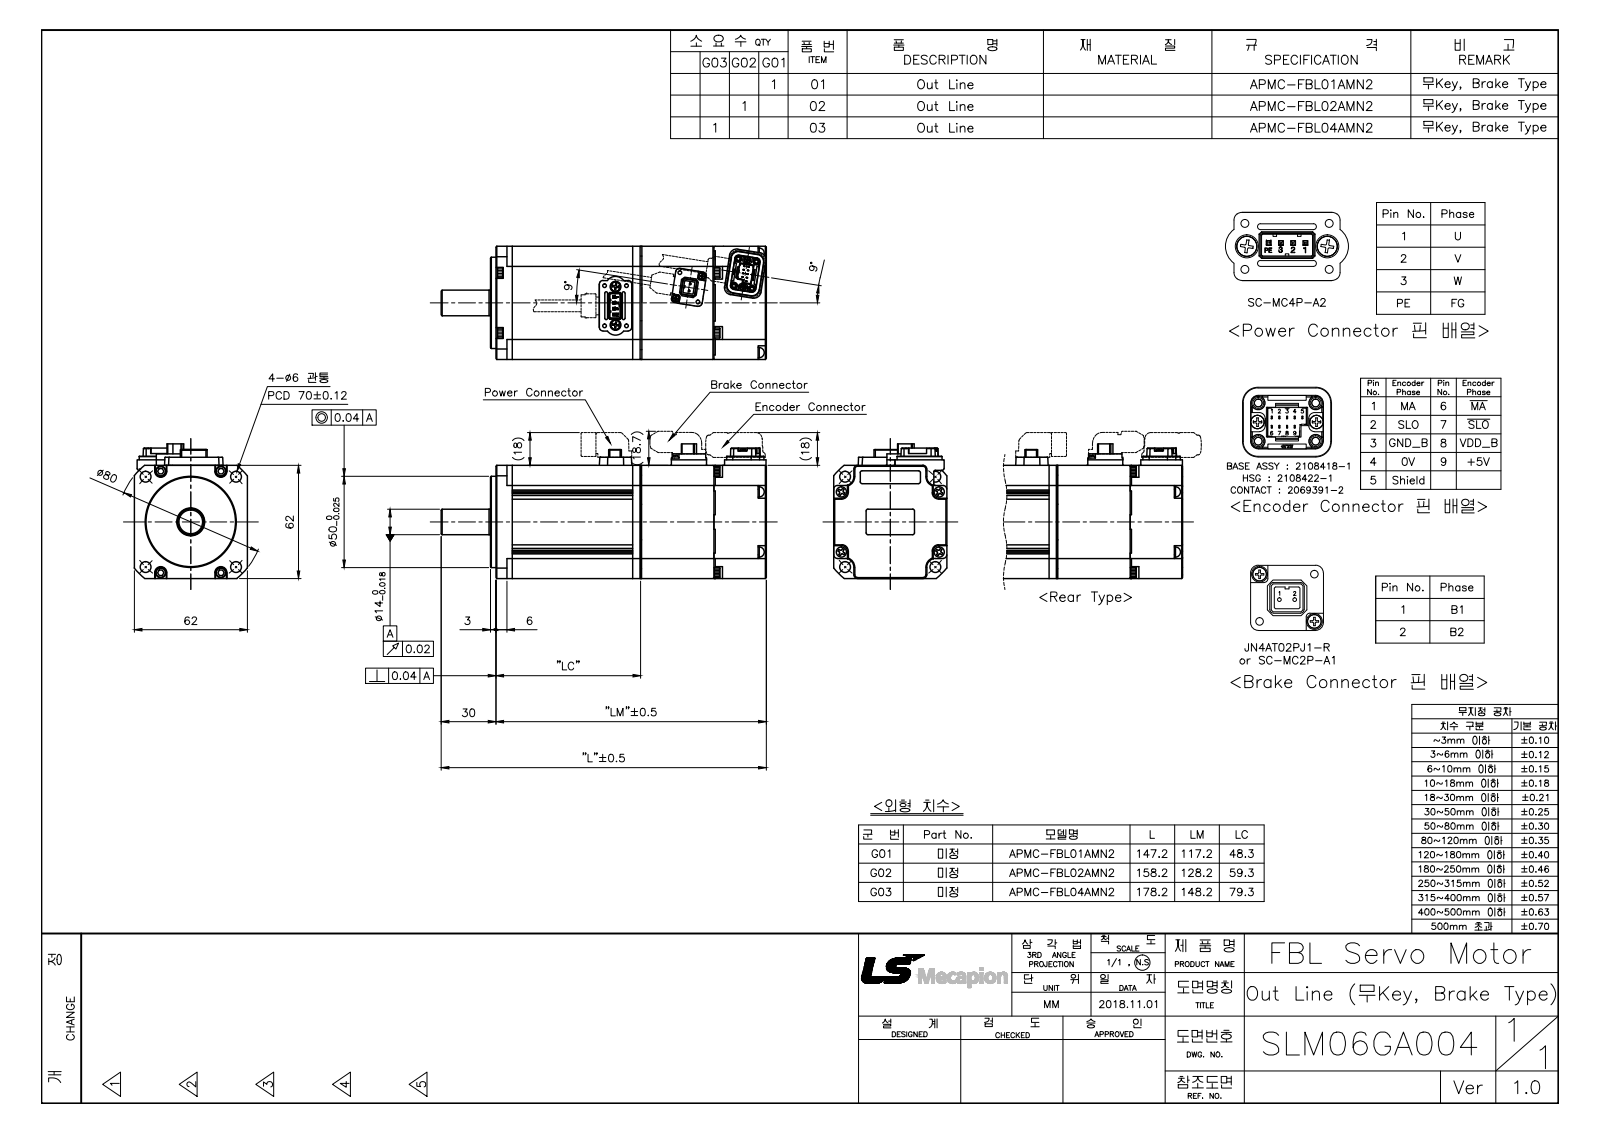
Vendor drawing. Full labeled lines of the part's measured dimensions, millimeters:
Part name (STEP PRODUCT): SLM06GA004G01_Out Line(APMC-FBL01AMN2)
STEP written by: SolidWorks 2011 (AUTOMOTIVE_DESIGN)
Units: millimetres
Bodies: 50 solids, 2073 faces (1276 planar, 578 cylindrical, 219 other)
Overall size (bounding box): 147.2 × 73.8 × 62
Volume: 411 727 mm³ · Surface area: 95 419 mm²
Round holes (diameter × count): ⌀2.1 ×10, ⌀3 ×10, ⌀3.5 ×8, ⌀2 ×6, ⌀6 ×6, ⌀3.1 ×4, ⌀1 ×2, ⌀3.3 ×1, ⌀3.4 ×1, ⌀13 ×1, ⌀15.3 ×1
Round bosses / shafts (diameter × count): ⌀5.4 ×6, ⌀5.6 ×4, ⌀5.5 ×4, ⌀4.2 ×2, ⌀3.6 ×2, ⌀3.5 ×2, ⌀2.2 ×2, ⌀0.9 ×2
Partial cylindrical surfaces — rounded edges, fillets, slot ends (radius × count): R0.2 ×20, R0.3 ×20, R1 ×14, R2 ×12, R0.15 ×9, R3 ×8, R0.45 ×7, R0.11 ×6
Main face-to-face distances: 62, 4.3, 0.5, 0.7, 35, 39.3, 44.5, 40.2, 79.5, 40.9
Hole centre spacings: 6.02, 8.5, 8.8, 9.43, 15.29, 16.01, 22.32, 31.47
